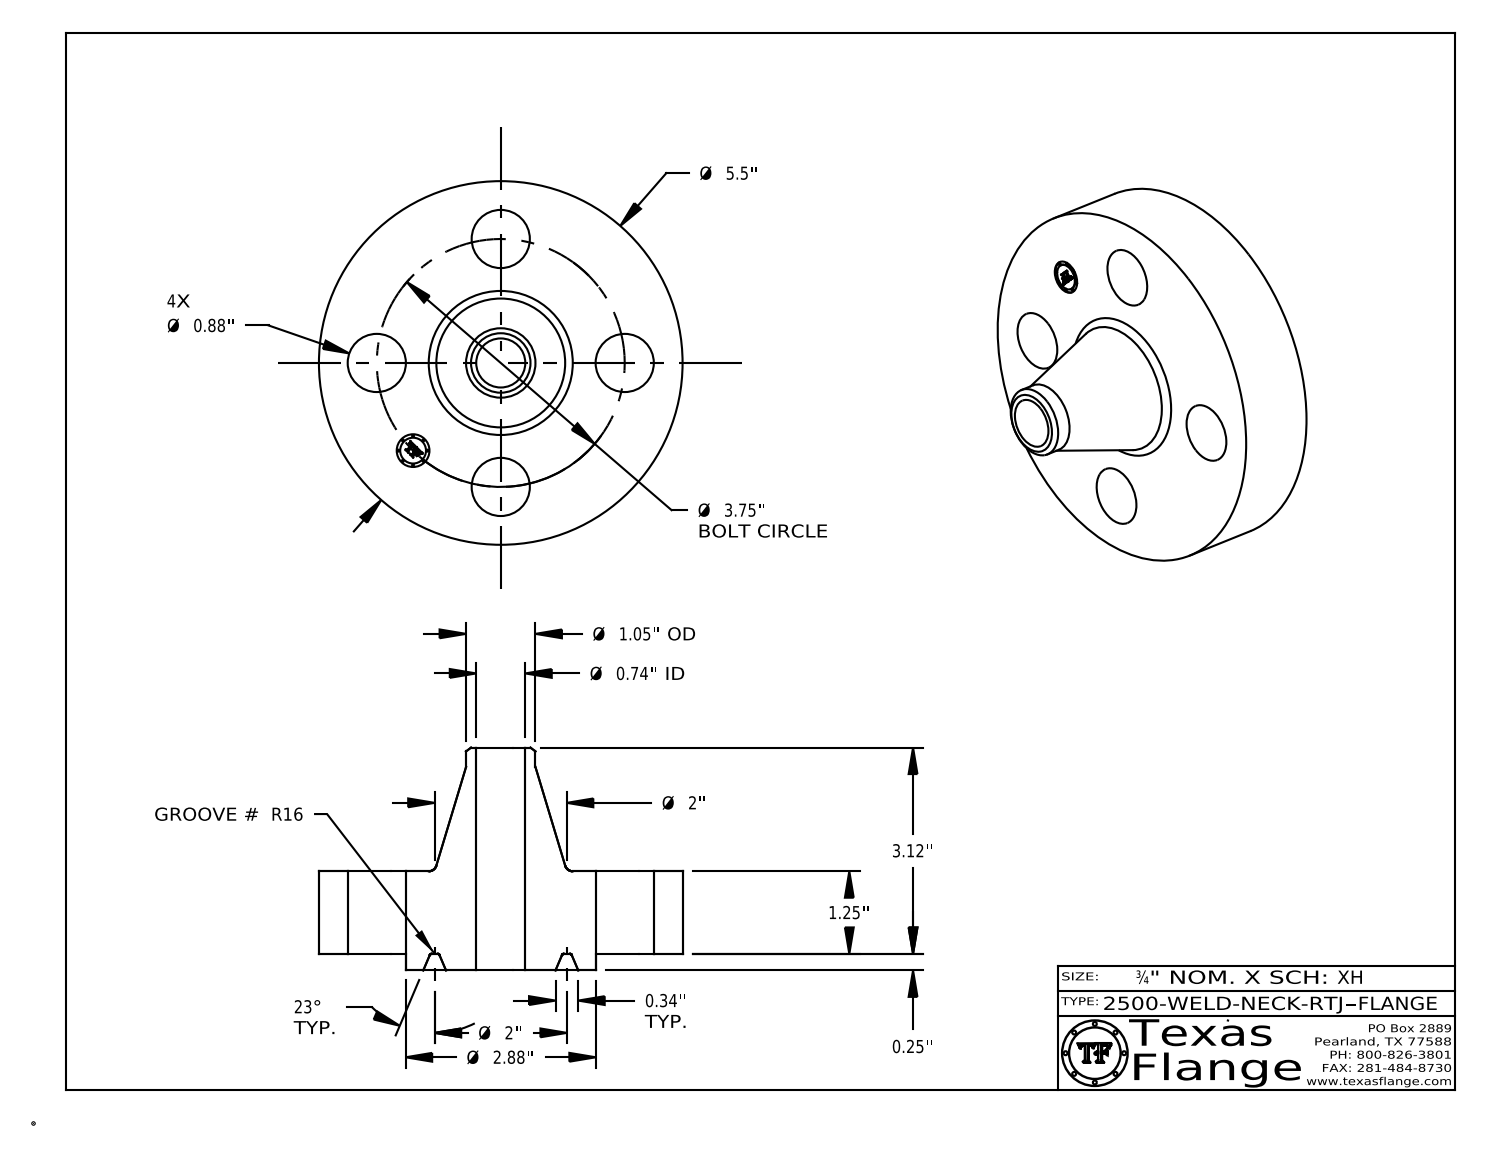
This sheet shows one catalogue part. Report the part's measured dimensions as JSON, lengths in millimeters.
{"part_name": "2500-WELD-NECK-RTJ", "step_written_by": "CATIA V5 STEP AP214 (AUTOMOTIVE_DESIGN)", "units": "millimeters", "bodies": {"solids": 1, "faces": 425, "planar": 371, "cylindrical": 40, "other": 14}, "overall_size": [139.7, 139.7, 85.6], "volume_mm3": 486400, "surface_area_mm2": 61760, "round_holes": [[22.4, 4], [12.6, 1], [18.8, 1]], "round_bosses_or_shafts": [[0.8, 8], [139.7, 1], [73, 1], [26.7, 1], [9.9, 1]], "face_to_face_distances": [31.8, 6.4, 38.1, 85.6, 79.2, 47.5, 37.7, 31.4, 0.4, 47.9], "hole_center_spacings": [47.6, 67.4, 36.4, 88, 95.3]}
